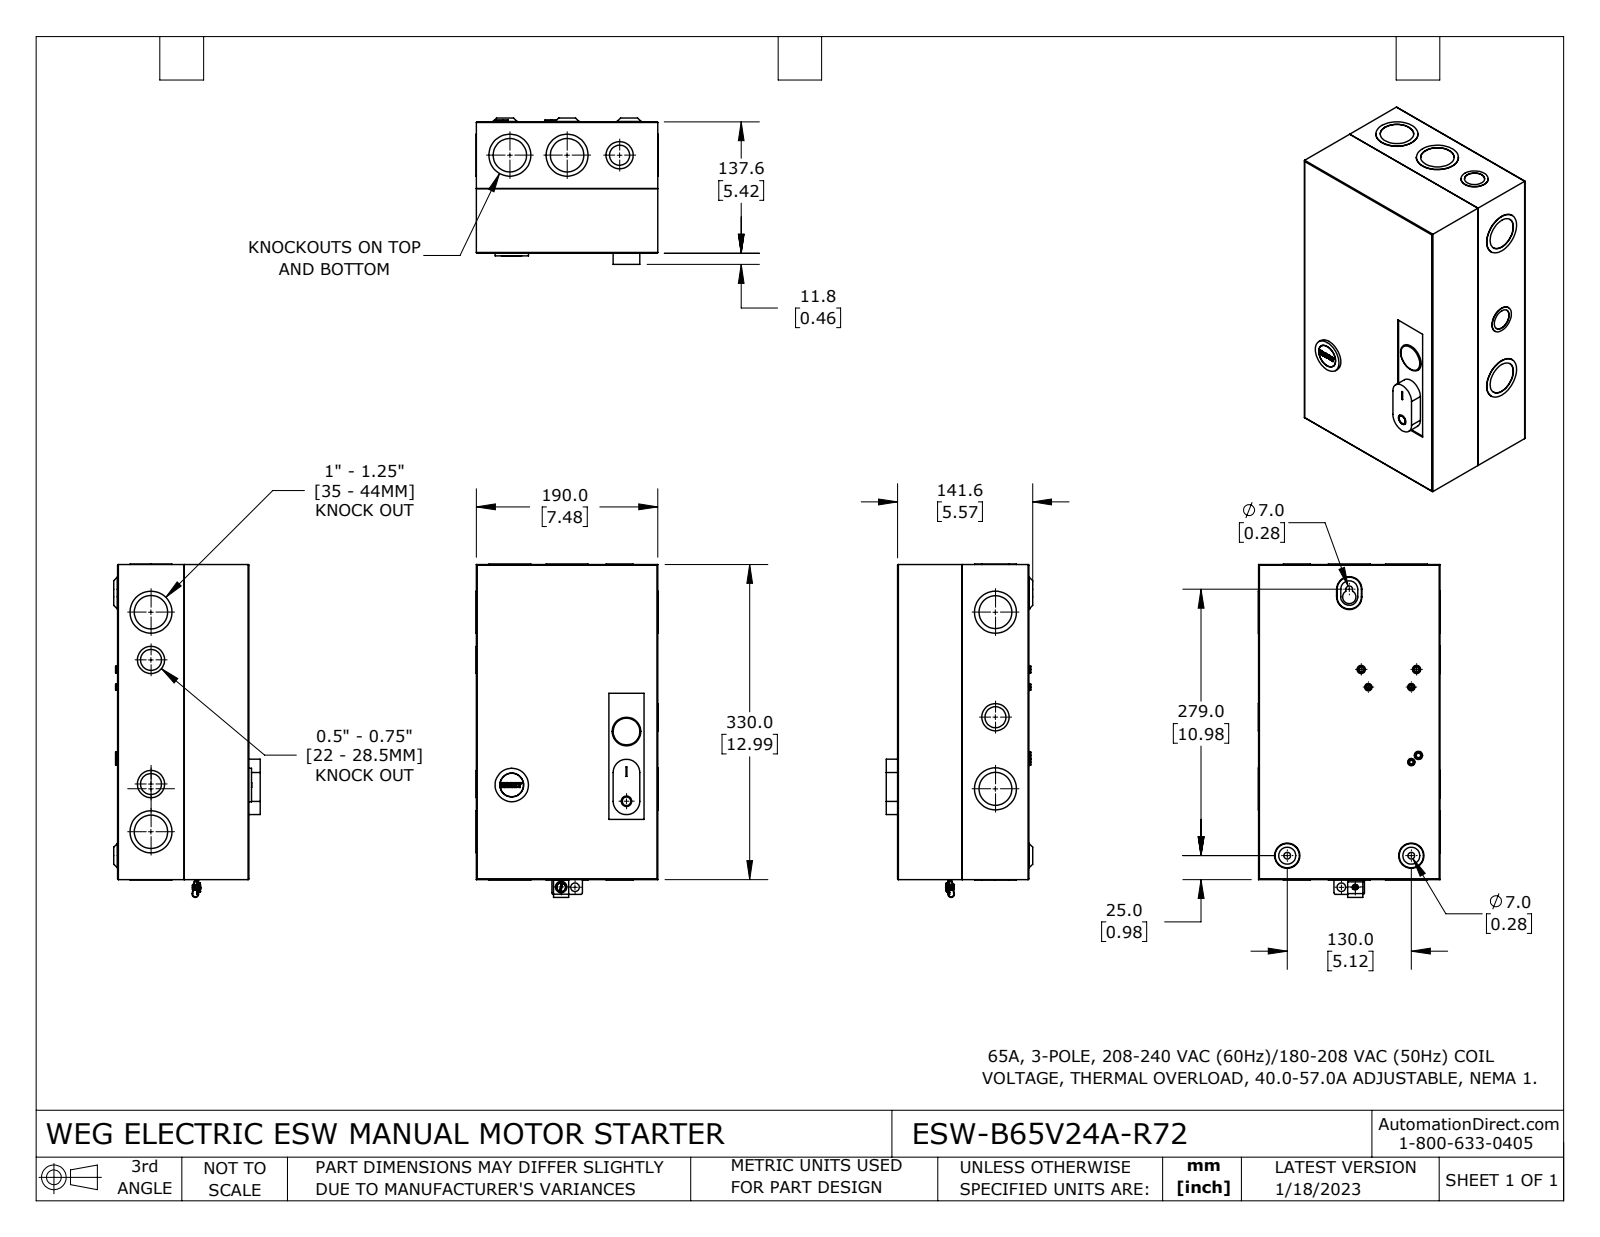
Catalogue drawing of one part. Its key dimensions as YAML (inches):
part_name: "ESW-B65V24A-R72"
step_written_by: "SolidWorks 2021 (CONFIG_CONTROL_DESIGN)"
units: inches
bodies: {solids: 7, faces: 435, planar: 161, cylindrical: 221, other: 53}
overall_size: [13.74, 7.504, 6.039]
volume: 24.58
surface_area: 936.7
round_holes:
  - {diameter: 1.378, count: 4}
  - {diameter: 0.146, count: 3}
  - {diameter: 0.183, count: 3}
  - {diameter: 0.276, count: 2}
  - {diameter: 0.866, count: 2}
  - {diameter: 0.886, count: 2}
  - {diameter: 1.357, count: 2}
  - {diameter: 0.256, count: 1}
  - {diameter: 0.279, count: 1}
  - {diameter: 0.354, count: 1}
  - {diameter: 0.433, count: 1}
  - {diameter: 0.469, count: 1}
round_bosses_or_shafts:
  - {diameter: 1.732, count: 4}
  - {diameter: 1.122, count: 3}
  - {diameter: 0.278, count: 3}
  - {diameter: 0.24, count: 3}
  - {diameter: 1.734, count: 2}
  - {diameter: 1.378, count: 1}
  - {diameter: 1.193, count: 1}
  - {diameter: 1.148, count: 1}
partial_cylinders:
  - {radius: 0.004, count: 34}
  - {radius: 0.031, count: 8}
  - {radius: 0.079, count: 3}
  - {radius: 0.138, count: 3}
  - {radius: 0.059, count: 2}
  - {radius: 0.075, count: 2}
  - {radius: 0.108, count: 2}
  - {radius: 0.122, count: 2}
face_to_face_distances: [0.047, 5.37, 7.433, 5.323, 5.417, 12.945, 7.386, 7.48, 0.071, 12.898]
hole_center_spacings: [0.571, 1.772, 1.969, 2.283, 2.362, 5.118, 7.087, 10.972]
